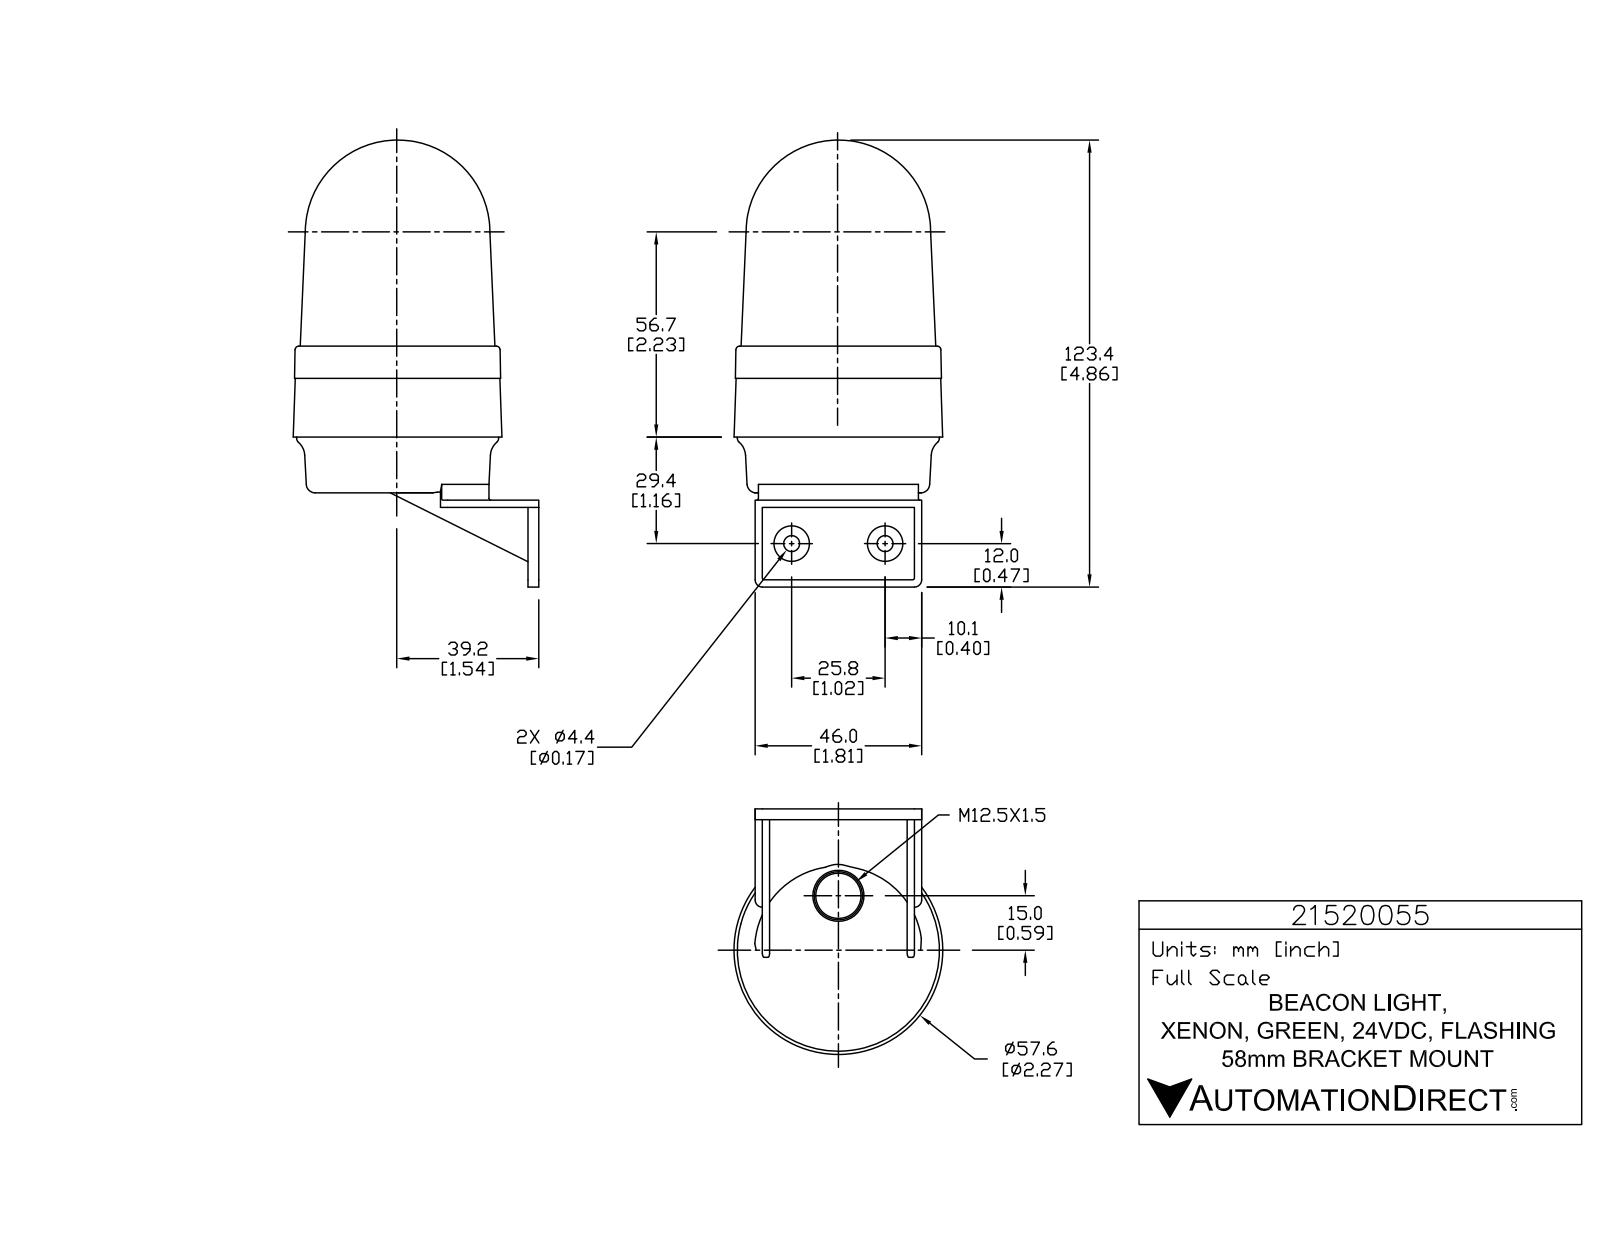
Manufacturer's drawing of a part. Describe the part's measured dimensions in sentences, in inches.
The part is named "21520055". Its 3-D file was written by "SolidWorks 2015 (AUTOMOTIVE_DESIGN)". It is 1 solid with 828 faces: 551 planar, 179 cylindrical and 98 other. Overall it measures 4.858 by 2.852 by 2.407 inches. Its volume is 12.43 cubic inches and its surface area 37.49 square inches. Round holes: 3 of diameter 0.039, 2 of diameter 0.173. Round bosses or shafts: 3 of diameter 0.226, 3 of diameter 0.056, 2 of diameter 0.386, 1 of diameter 2.197. Partial cylindrical surfaces (rounded edges, fillets, slot ends): 6 of radius 0.008, 6 of radius 0.008, 6 of radius 0.008, 6 of radius 0.02, 6 of radius 0.131, 4 of radius 0.079, 3 of radius 0.004, 3 of radius 0.005. The main face-to-face distances are 0.079, 0.157, 1.575, 1.654, 0.039, 0.118, 1.496, 0.866, 0.945, 0.764. The hole center spacings are 1.016.
